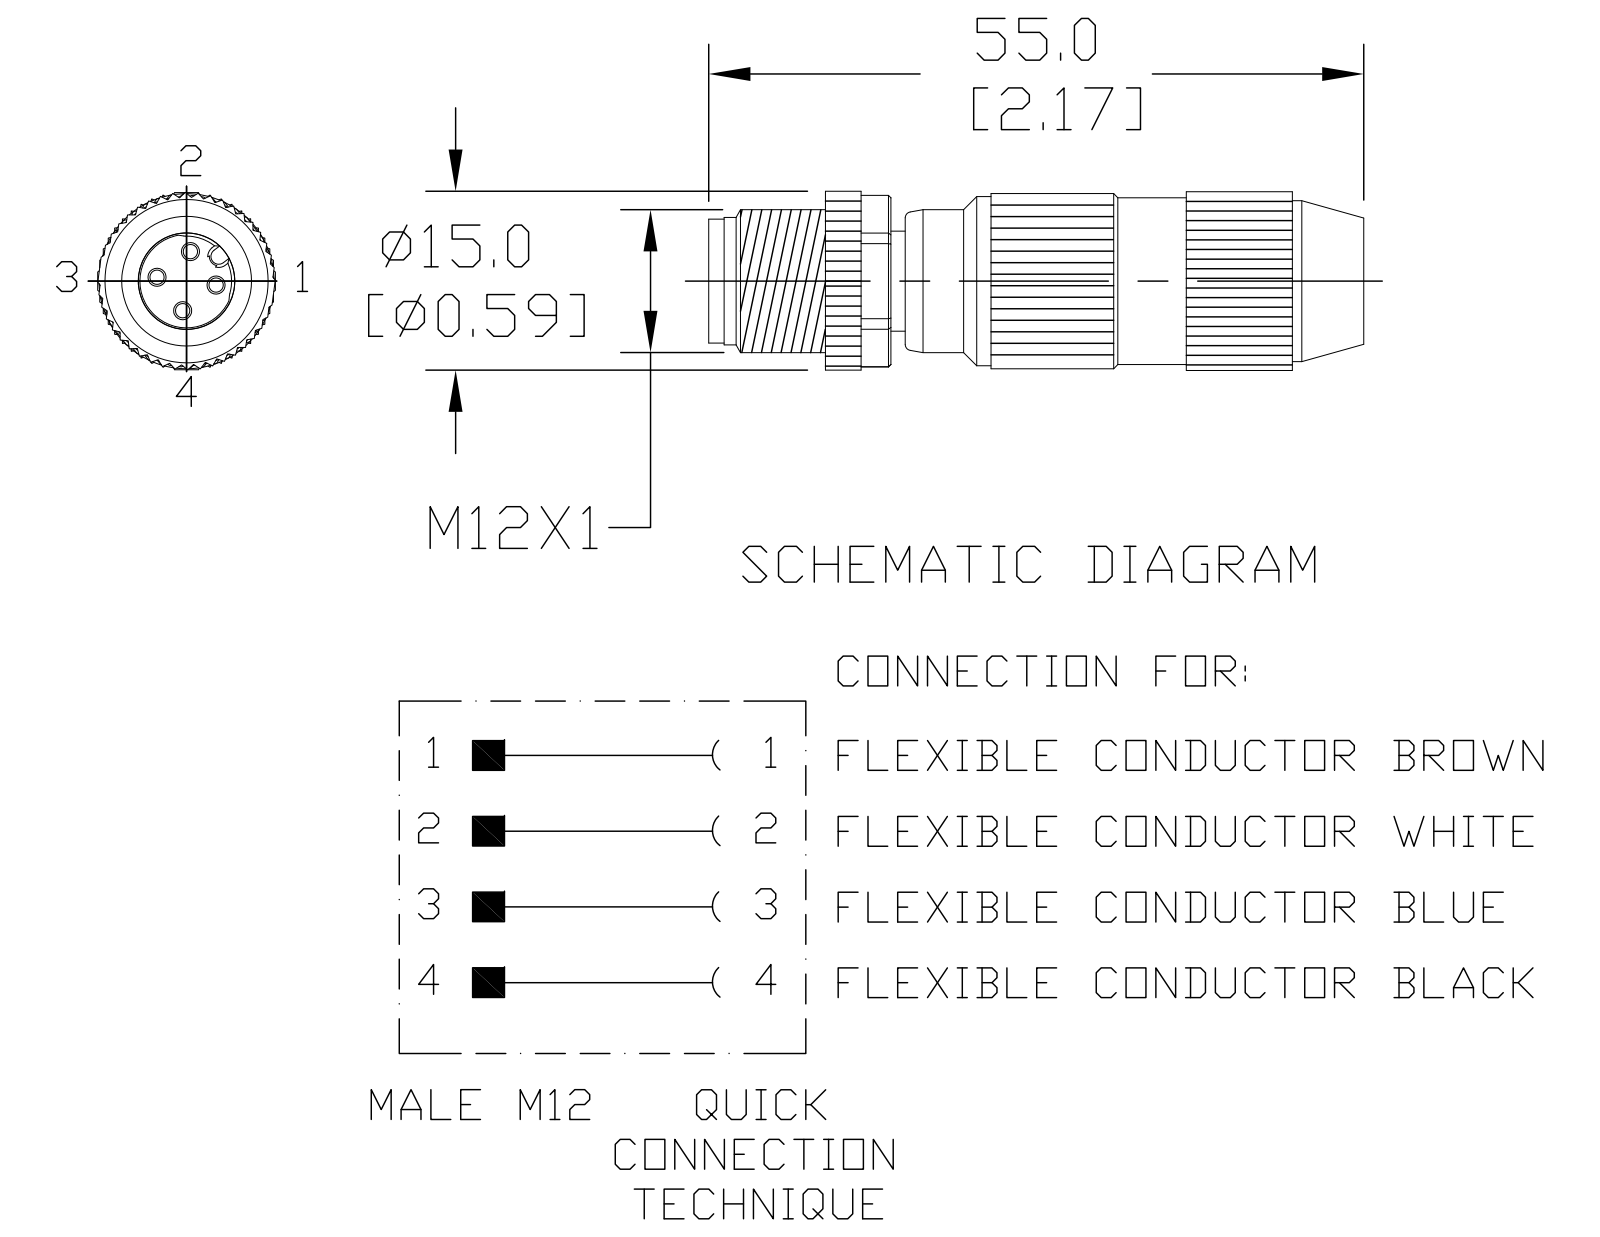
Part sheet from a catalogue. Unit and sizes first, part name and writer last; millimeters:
Units: millimetres
Overall size (bounding box): 1295.4 × 381 × 381
Round holes (diameter × count): ⌀154.9 ×1, ⌀219.2 ×1
Round bosses / shafts (diameter × count): ⌀25.4 ×4, ⌀381 ×1, ⌀351.2 ×1, ⌀345.4 ×1, ⌀304.8 ×1, ⌀280.9 ×1, ⌀264.2 ×1, ⌀246.9 ×1
Partial cylindrical surfaces — rounded edges, fillets, slot ends (radius × count): R190.4 ×1
Main face-to-face distances: 50.8, 420, 139.7, 1041.4, 990.6, 1130.3, 307.3, 88.9, 621.4, 369.2
Volume: 103 200 000 mm³ · Surface area: 2 568 000 mm²
Bodies: 1 solid, 539 faces (370 planar, 140 cylindrical, 29 other)
Part name (STEP PRODUCT): 7000-12481-0000000
STEP written by: SolidWorks 2015 (AUTOMOTIVE_DESIGN)
